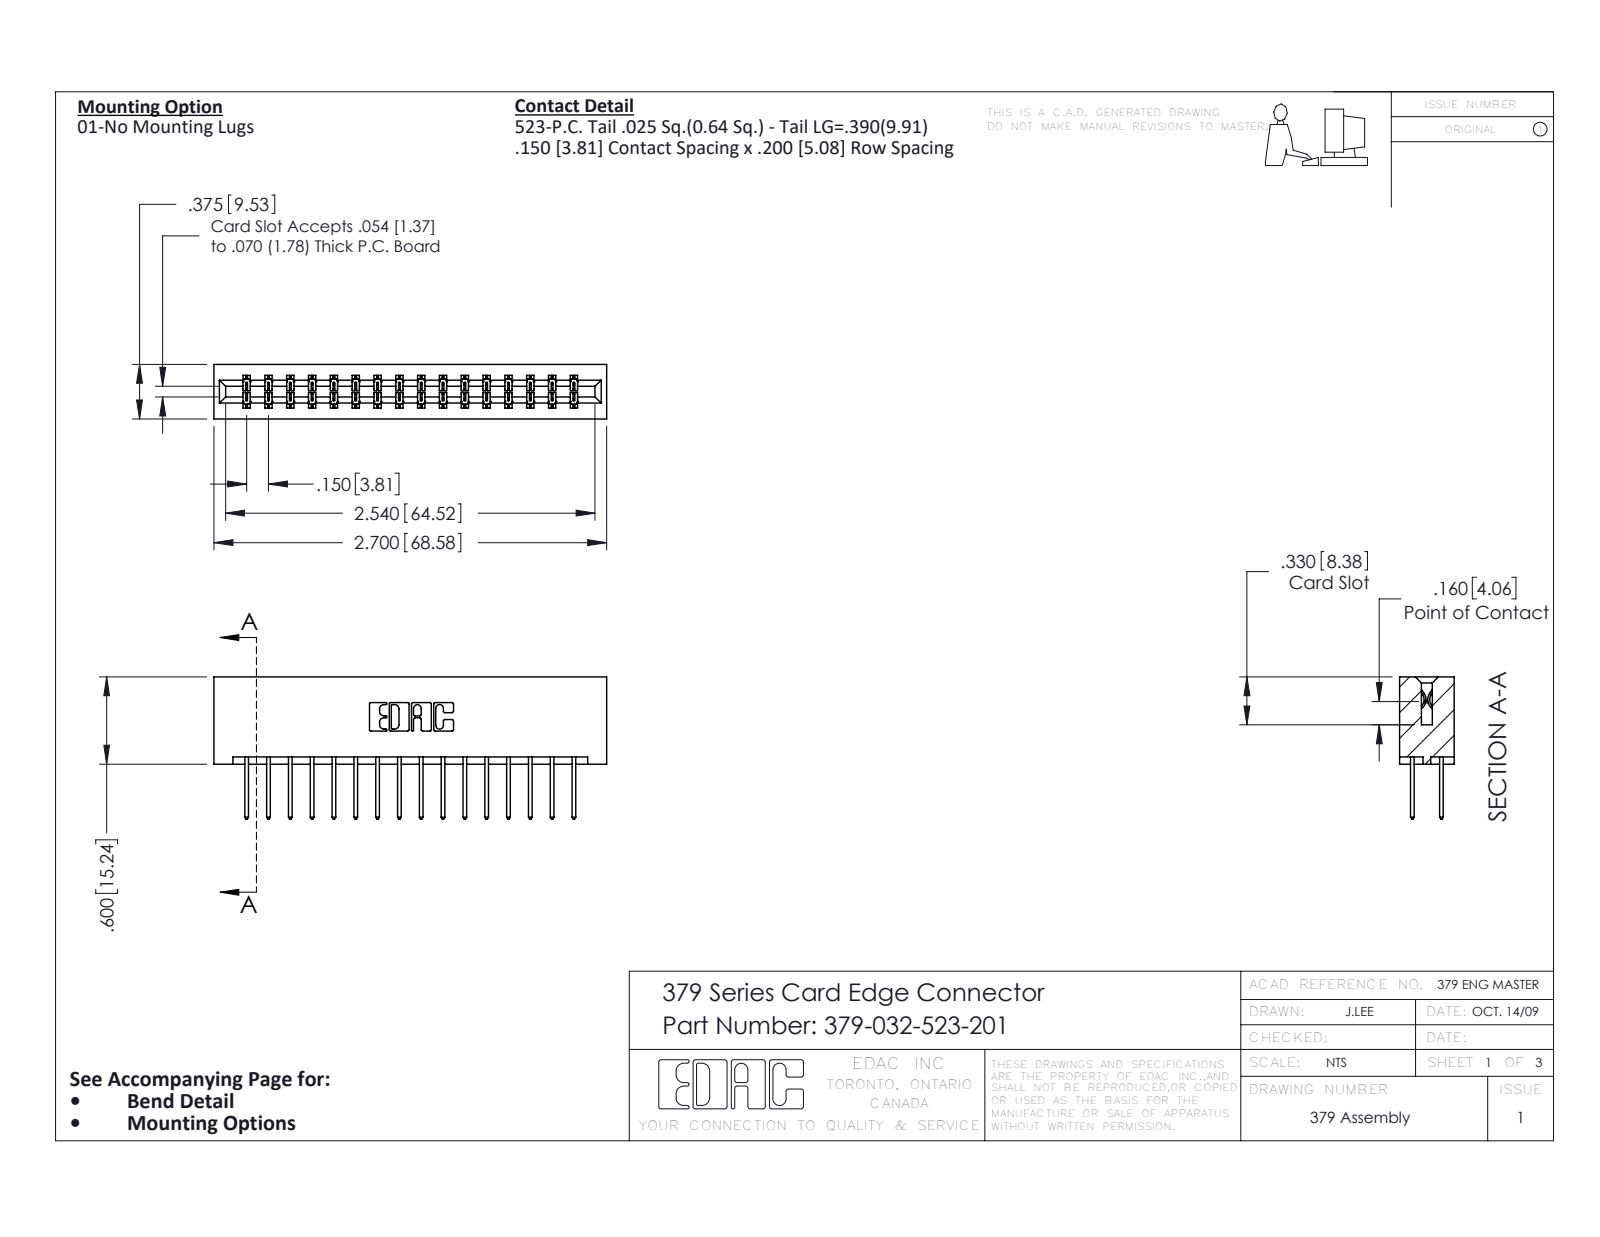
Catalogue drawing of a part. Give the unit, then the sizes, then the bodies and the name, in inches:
Units: inches
Overall size (bounding box): 2.7 × 0.977 × 0.375
Partial cylindrical surfaces — rounded edges, fillets, slot ends (radius × count): R0.006 ×48, R0.01 ×32, R0.01 ×22, R0.007 ×6, R0.031 ×6, R0.026 ×3, R0.014 ×2, R0.022 ×2
Main face-to-face distances: 0.3, 0.075, 0.2, 0.1, 0.375, 0.15, 0.55, 0.6, 0.225, 0.275
Volume: 0.475 in³ · Surface area: 13.73 in²
Bodies: 33 solids, 1770 faces (1218 planar, 552 cylindrical, 0 other)
Part name (STEP PRODUCT): 345-292-001_345-293-123; 379 Part_Lugless; 379-032-523-201
STEP written by: SolidWorks 2020 (CONFIG_CONTROL_DESIGN)
